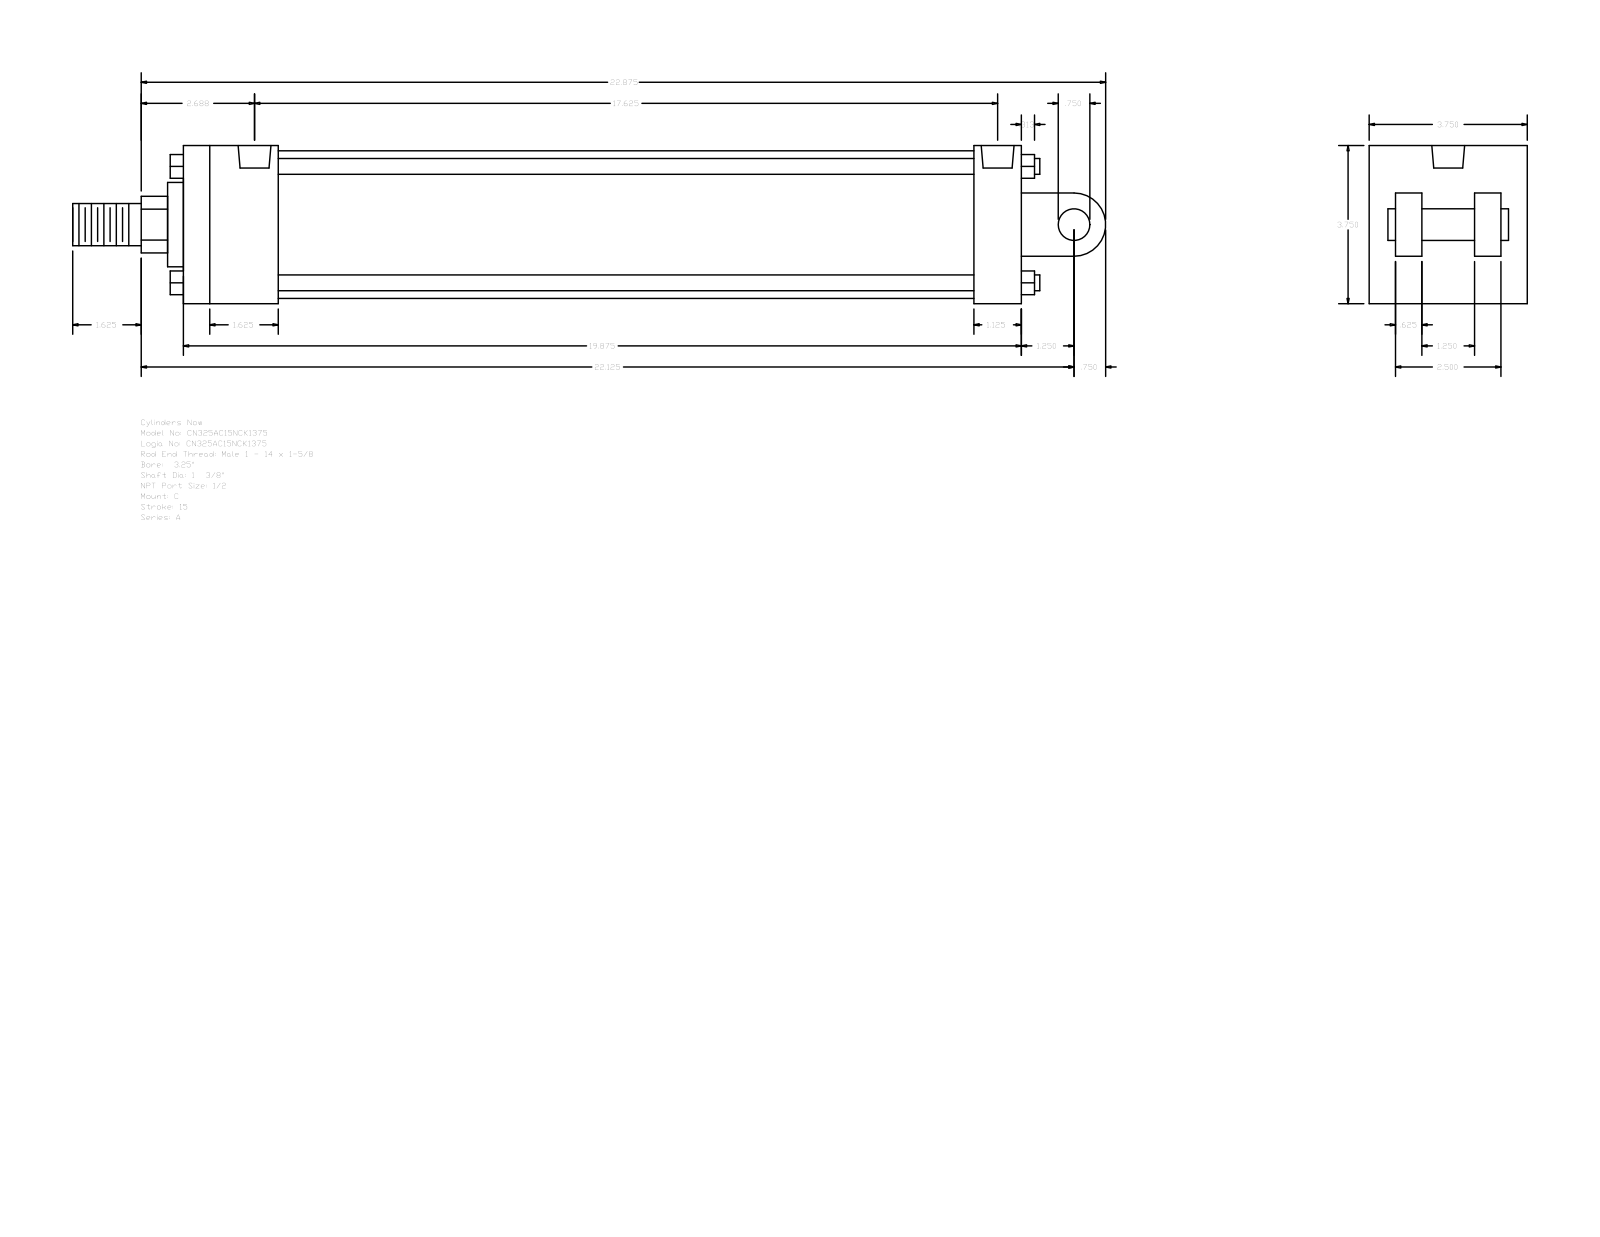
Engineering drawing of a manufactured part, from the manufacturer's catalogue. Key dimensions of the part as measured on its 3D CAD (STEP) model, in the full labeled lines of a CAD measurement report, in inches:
Part name (STEP PRODUCT): A_C__0325_1.375
STEP written by: GSSL Pune (CONFIG_CONTROL_DESIGN)
Units: inches
Bodies: 0 solids, 135 faces (102 planar, 33 cylindrical, 0 other)
Overall size (bounding box): 24.5 × 3.75 × 3.75
Round holes (diameter × count): ⌀0.344 ×4, ⌀0.778 ×2
Round bosses / shafts (diameter × count): ⌀0.375 ×4, ⌀3.5 ×1, ⌀2 ×1, ⌀1.375 ×1, ⌀1 ×1, ⌀0.75 ×1
Partial cylindrical surfaces — rounded edges, fillets, slot ends (radius × count): R0.672 ×1, R0.75 ×1
Main face-to-face distances: 3.75, 19.875, 0.625, 2.5, 2.625, 2.25, 1.125, 1.25, 3.125, 1.875
Hole centre spacings: 0.125, 17.375, 17.5, 17.625
